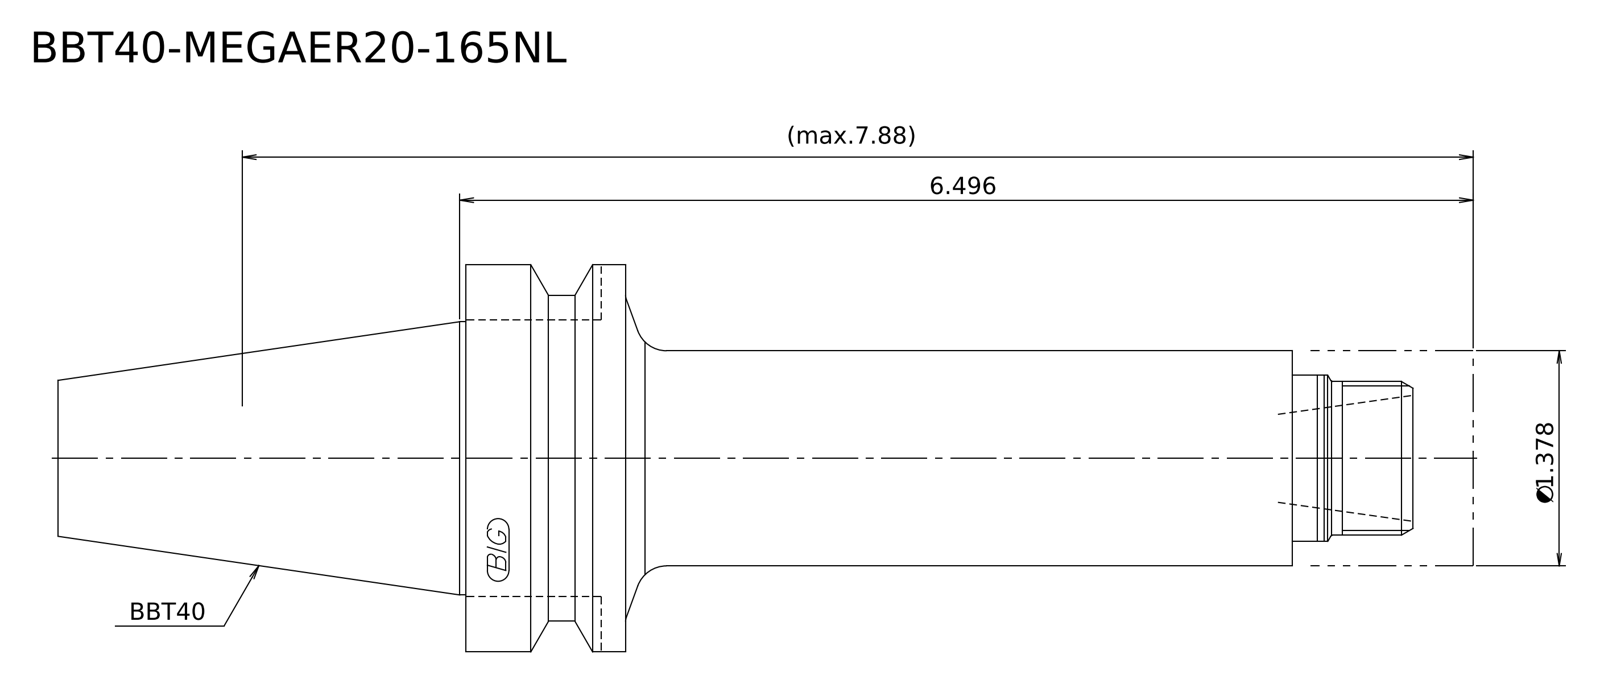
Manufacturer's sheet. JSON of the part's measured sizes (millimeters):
{"step_written_by": "Kubotek KeyCreator 2011 V10.0.2 (22737) (automotive_design)", "units": "millimeters", "bodies": {"solids": 2, "faces": 21, "planar": 7, "cylindrical": 8, "other": 6}, "overall_size": [230.4, 63, 63], "volume_mm3": 284006, "surface_area_mm2": 36372, "round_bosses_or_shafts": [[63, 1], [53, 1], [44.45, 1], [35, 1], [27, 1], [25, 1]], "face_to_face_distances": [26.5, 164, 137.5, 138, 111.5, 26, 230.4, 203.9, 92.4, 66.4]}
